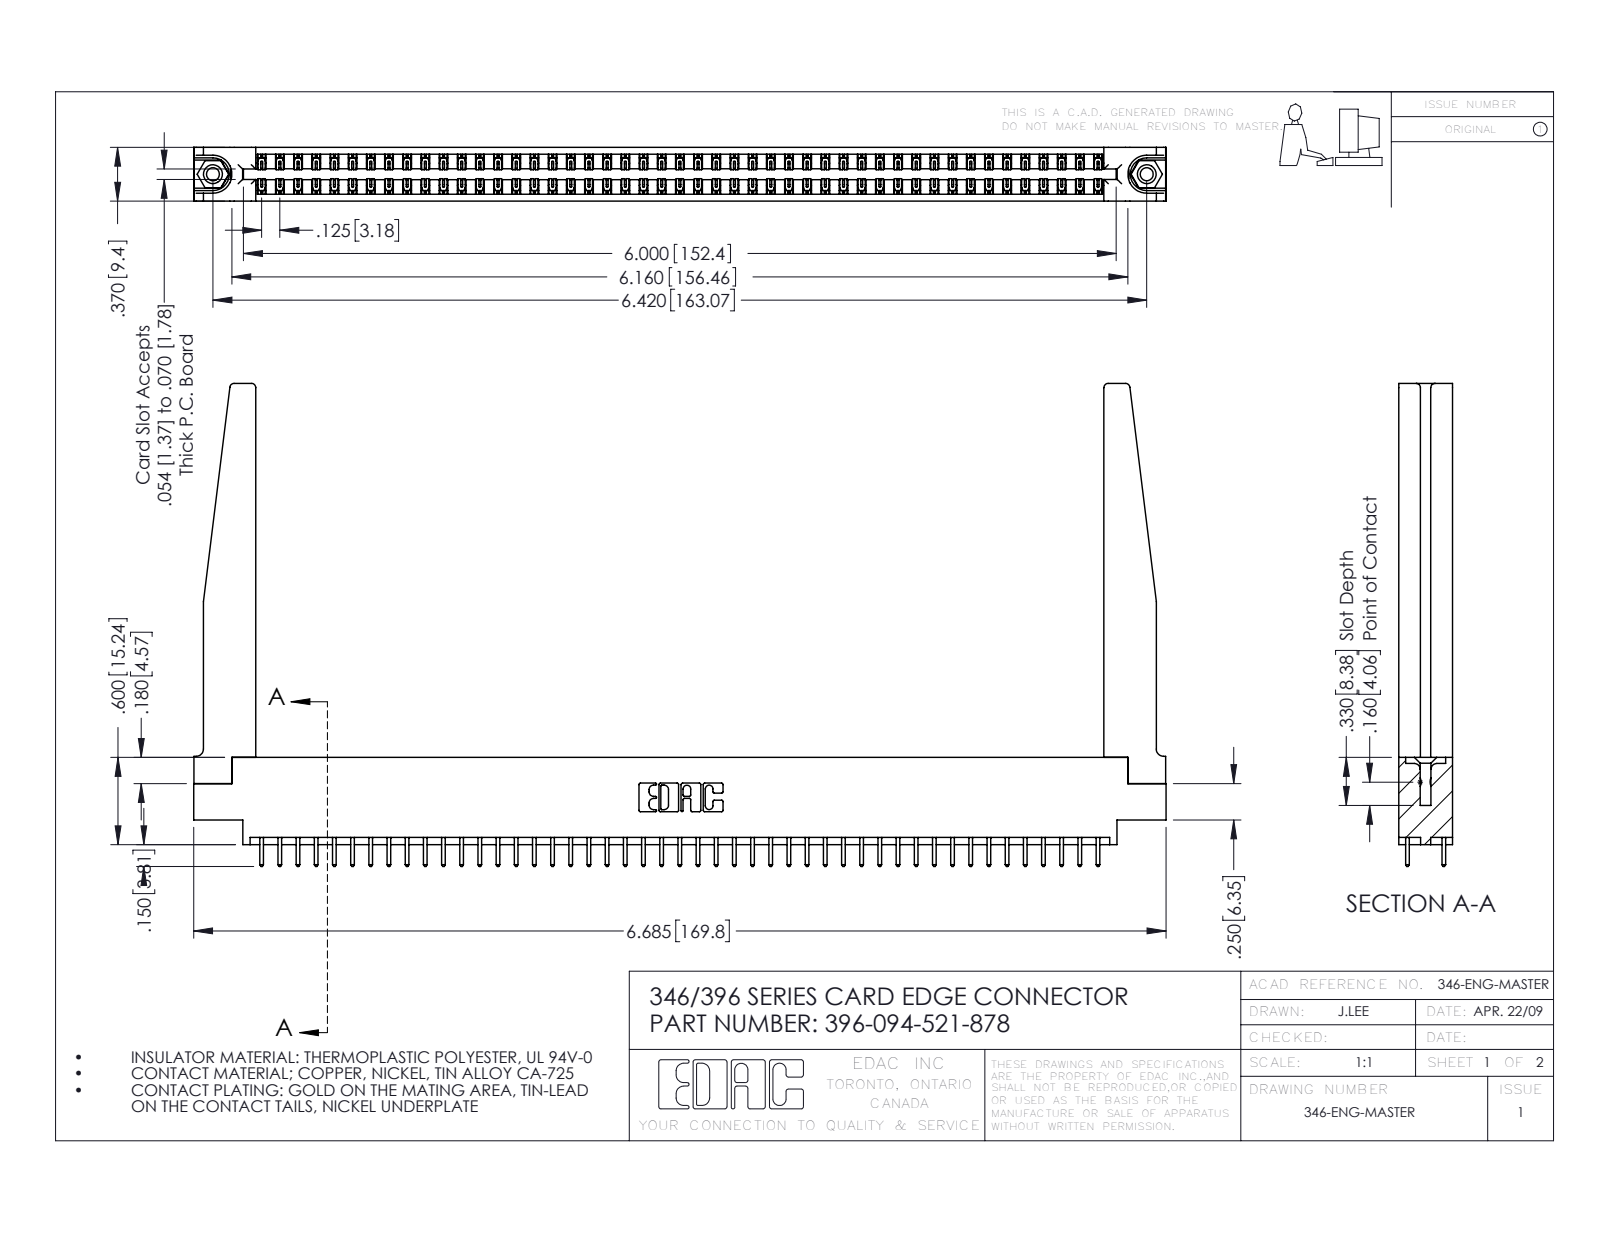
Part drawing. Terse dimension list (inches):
name: 345-292-001_345-293-121; 346-220-078_345-220-078; 346 Part_0.170 Offset - 0.156 Dia-TH; 396-094-521-878 (+1 more)
written by: SolidWorks 2016 (CONFIG_CONTROL_DESIGN)
unit: in
bodies: 99 solids, 5248 faces (3512 planar, 1684 cylindrical, 52 other)
size: 6.685 × 3.32 × 0.37
volume: 1.423 in³; area: 45.08 in²
holes: 2× ⌀0.089, 2× ⌀0.125, 2× ⌀0.156, 1× ⌀0.064
bosses: 2× ⌀0.155
rounds: 141× R0.006, 94× R0.01, 22× R0.01, 8× R0.03, 6× R0.007, 6× R0.031, 3× R0.026, 2× R0.014
face distances: 0.37, 0.048, 0.322, 0.072, 0.25, 0.15, 0.148, 0.298, 0.025, 0.275
hole spacings: 0.246, 6.211, 6.42
